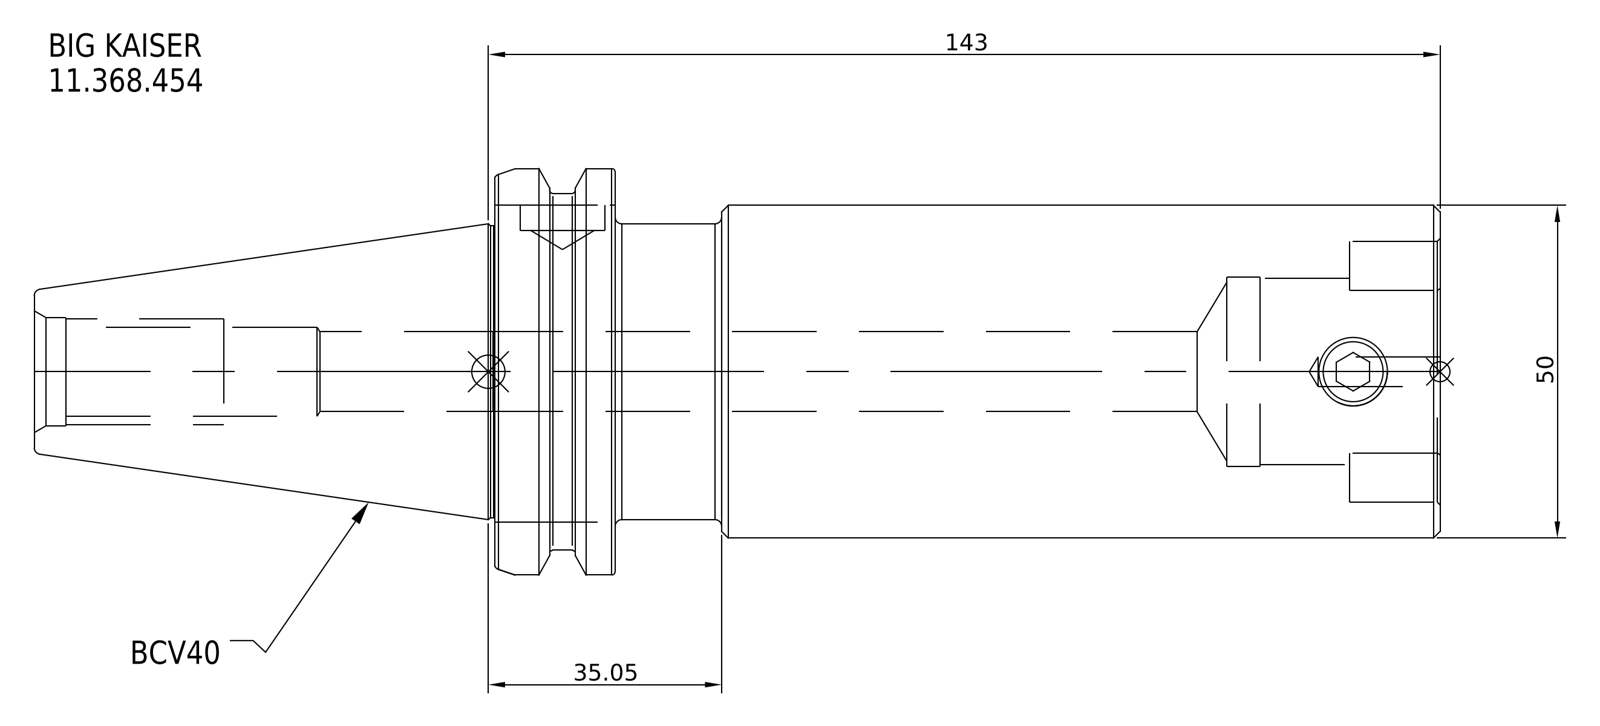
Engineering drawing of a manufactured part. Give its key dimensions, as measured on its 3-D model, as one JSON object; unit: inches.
{"part_name": "11.368.454", "step_written_by": "SolidWorks 2021 (CONFIG_CONTROL_DESIGN)", "units": "inches", "bodies": {"solids": 1, "faces": 16, "planar": 7, "cylindrical": 6, "other": 3}, "overall_size": [8.317, 2.5, 2.5], "volume_in3": 21.61, "surface_area_in2": 57.56, "round_bosses_or_shafts": [[2.5, 1], [2.219, 1], [1.969, 1], [1.75, 1]], "face_to_face_distances": [5.505, 4.88, 0.625, 8.317, 3.437, 2.812, 4.25, 0.63, 1.255, 4.067]}
